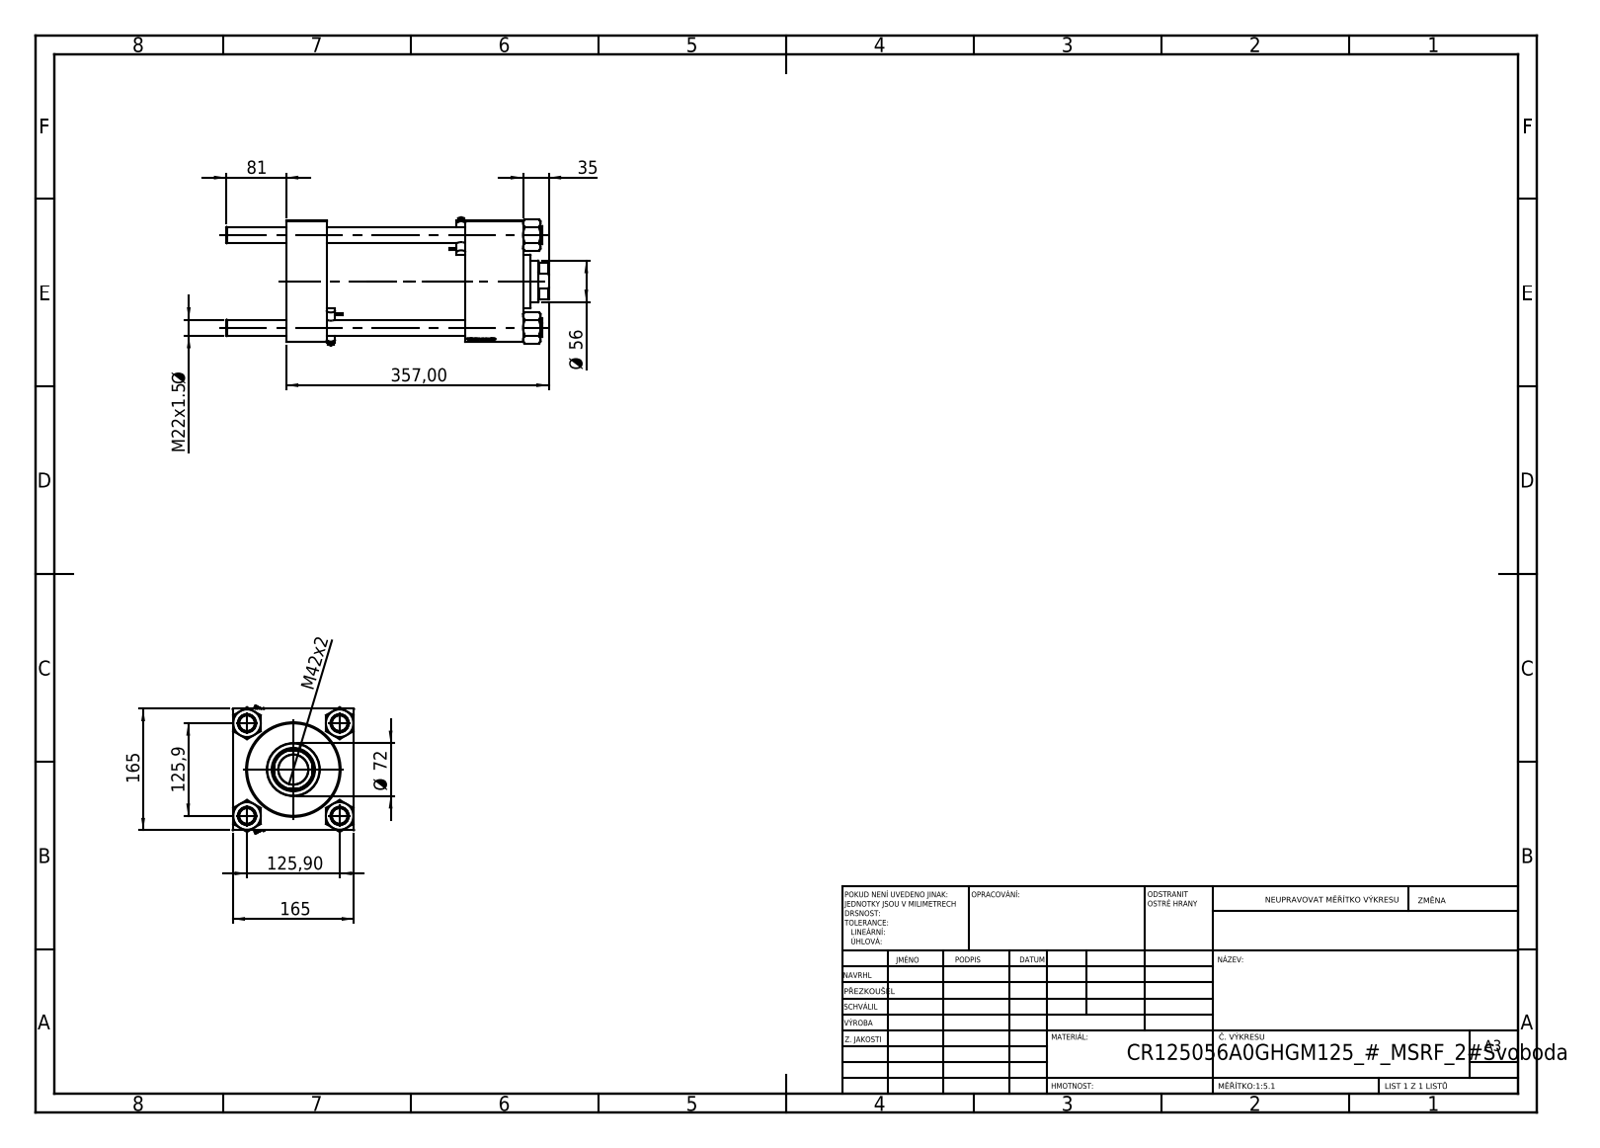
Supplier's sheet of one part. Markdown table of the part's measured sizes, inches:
| quantity | value |
| --- | --- |
| part name | V215CR_VCP; V215_VC_A; CR025_012_A_0_G_A_G_M_020_+#_##_TYCINKA; V215CR_BODY_A (+2 more) |
| STEP written by | SolidWorks 2019 (CONFIG_CONTROL_DESIGN) |
| units | inches |
| bodies | 13 solids, 1246 faces (604 planar, 106 cylindrical, 536 other) |
| overall size | 17.244 × 6.844 × 6.496 |
| volume | 319.4 in³ |
| surface area | 1 063 in² |
| round holes (diameter × count) | 0.866 × 4, 0.276 × 2, 1.269 × 2, 1.772 × 2, 1.594 × 1, 2.205 × 1, 2.323 × 1, 3.78 × 1, 4.921 × 1, 4.941 × 1 |
| round bosses / shafts (diameter × count) | 0.984 × 4, 0.197 × 2, 0.098 × 2, 5.157 × 1, 2.835 × 1 |
| partial cylindrical surfaces (radius × count) | 0.02 × 12, 0.236 × 4, 1.063 × 1 |
| main face-to-face distances | 6.496, 2.165, 12.677, 10.512, 9.606, 7.441, 3.071, 11.547, 9.382, 1.941 |
| hole center spacings | 3.505, 4.957, 7.01, 9.587 |
